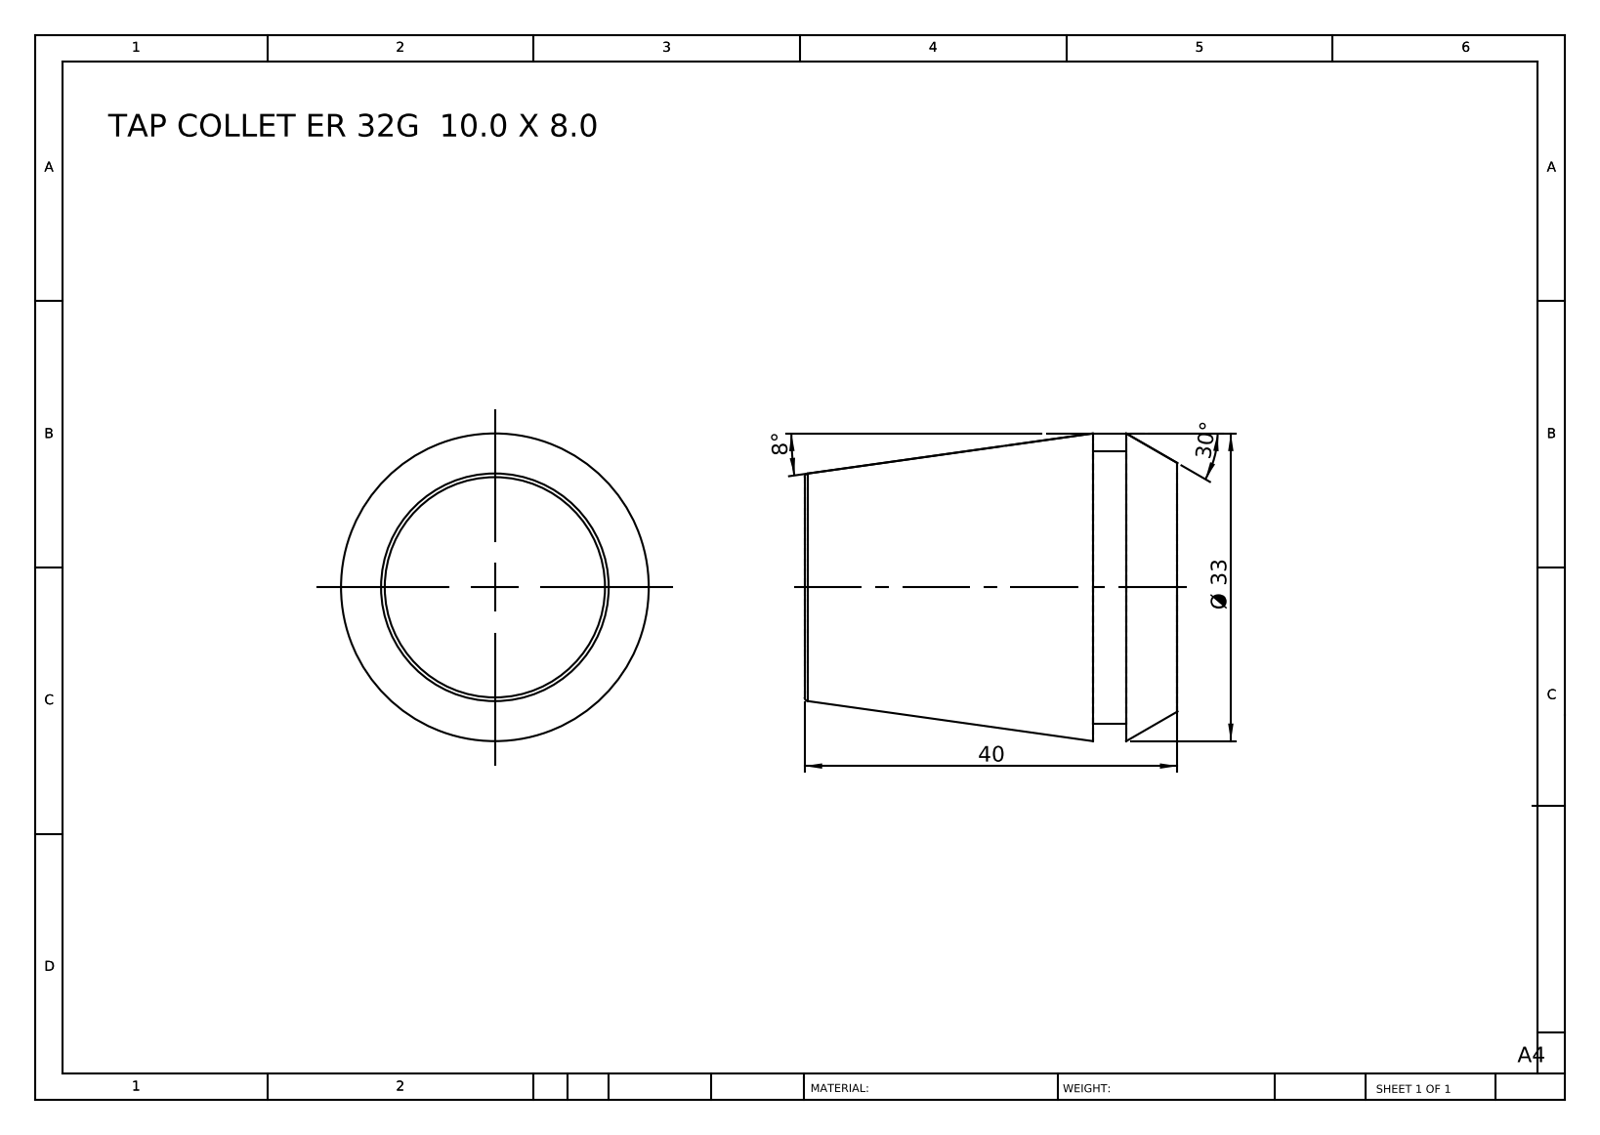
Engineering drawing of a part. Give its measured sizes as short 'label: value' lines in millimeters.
name: TAP COLLET ER 32G 10.0 X 8.0
written by: SolidWorks 2014 (CONFIG_CONTROL_DESIGN)
unit: mm
bodies: 1 solid, 12 faces (4 planar, 2 cylindrical, 6 other)
size: 40 × 33 × 33
volume: 26 350 mm³; area: 5 119 mm²
bosses: 1× ⌀29.2
face distances: 40, 9.1, 30.9, 5.5, 3.6, 34.5
